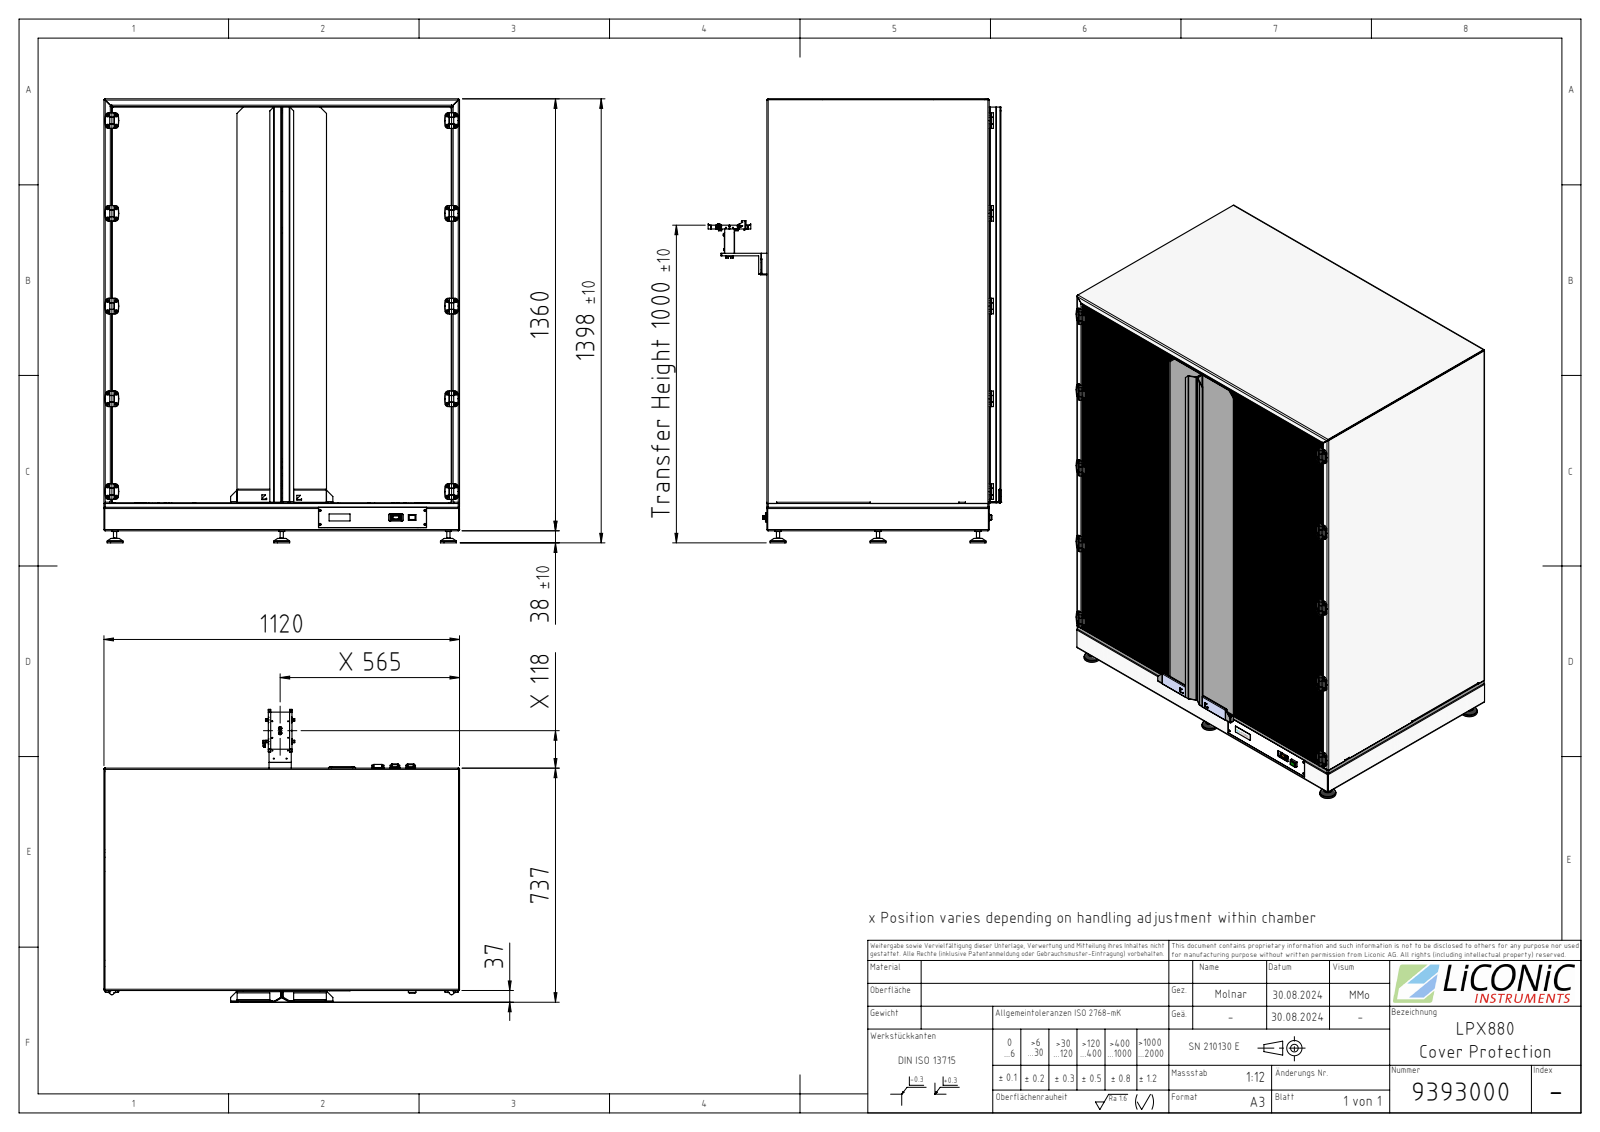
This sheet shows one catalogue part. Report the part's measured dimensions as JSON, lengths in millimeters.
{"part_name": "9393000", "step_written_by": "SolidWorks 2022 (AUTOMOTIVE_DESIGN)", "units": "millimeters", "bodies": {"solids": 104, "faces": 15196, "planar": 8009, "cylindrical": 6869, "other": 318}, "overall_size": [1398, 1120, 922.18], "volume_mm3": 33340000, "surface_area_mm2": 21150000, "round_holes": [[4, 176], [2.5, 86], [4.2, 73], [4.5, 56], [3.3, 51], [9, 45], [6, 36], [6.5, 34], [5.2, 22], [4.7, 16], [6.8, 16], [8.5, 16]], "round_bosses_or_shafts": [[22, 16], [50.01, 7], [10, 7], [1.5, 3], [540, 2], [234, 2], [13.5, 2], [15.5, 1]], "partial_cylinders_radius": [[0.1, 1660], [0.25, 1656], [2, 866], [2.5, 156], [1, 133], [5, 133], [4, 51], [1.5, 44]], "face_to_face_distances": [2, 1118, 700, 693, 698, 1358, 5, 695, 1120, 1116], "hole_center_spacings": [23, 46, 69, 92, 115, 138, 161, 62.5]}
